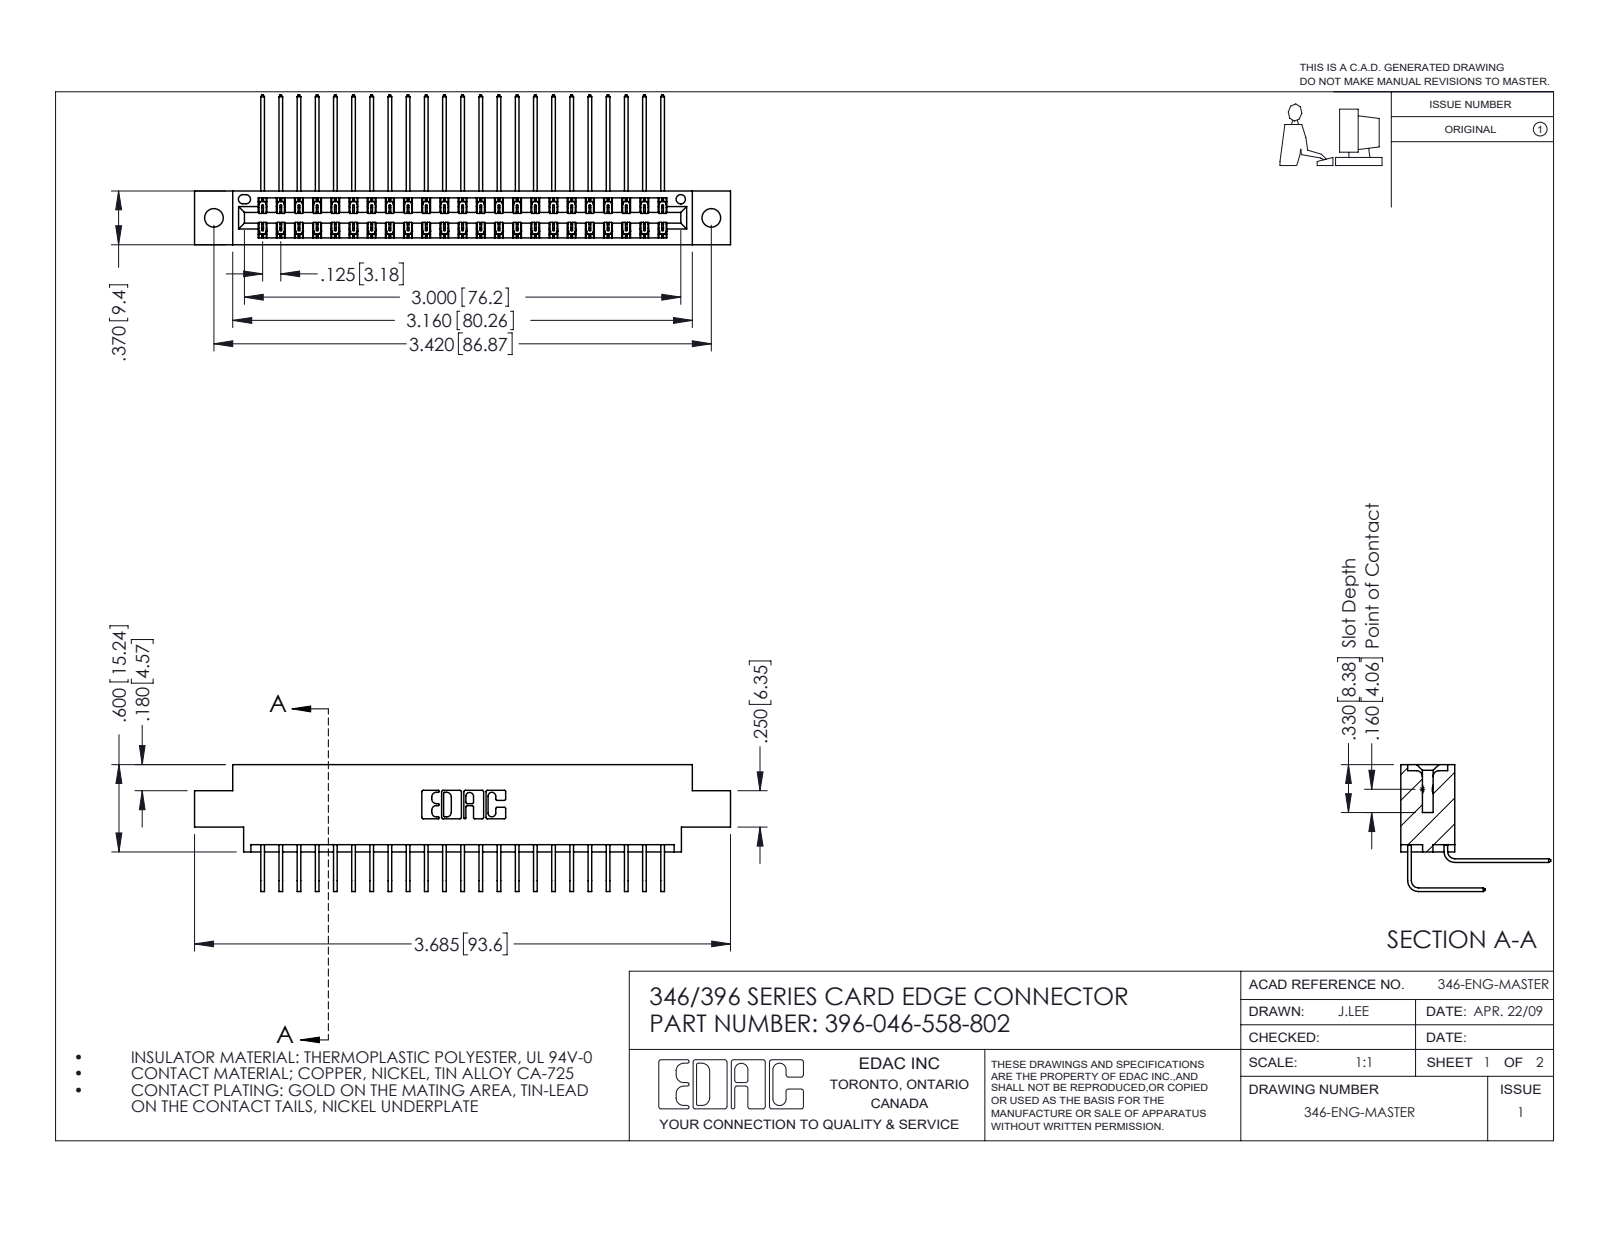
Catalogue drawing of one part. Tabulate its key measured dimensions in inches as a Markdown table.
| quantity | value |
| --- | --- |
| part name | 346 Part_0.170 Offset - 0.128 Dia; 396-046-558-802; 345-292-001_558 Tail - 2; 345-292-001_558 559 Tail - 1 |
| STEP written by | SolidWorks 2016 (CONFIG_CONTROL_DESIGN) |
| units | inches |
| bodies | 47 solids, 2610 faces (1782 planar, 828 cylindrical, 0 other) |
| overall size | 3.685 × 1.03 × 0.873 |
| volume | 0.552 in³ |
| surface area | 20.66 in² |
| round holes (diameter × count) | 0.128 × 2, 0.064 × 1 |
| partial cylindrical surfaces (radius × count) | 0.006 × 69, 0.01 × 22, 0.007 × 6, 0.031 × 6, 0.026 × 3, 0.014 × 2, 0.022 × 2, 0.024 × 2 |
| main face-to-face distances | 0.322, 0.048, 0.37, 0.025, 0.25, 0.298, 0.072, 0.275, 0.148, 0.222 |
| hole center spacings | 0.246, 3.212, 3.42 |
